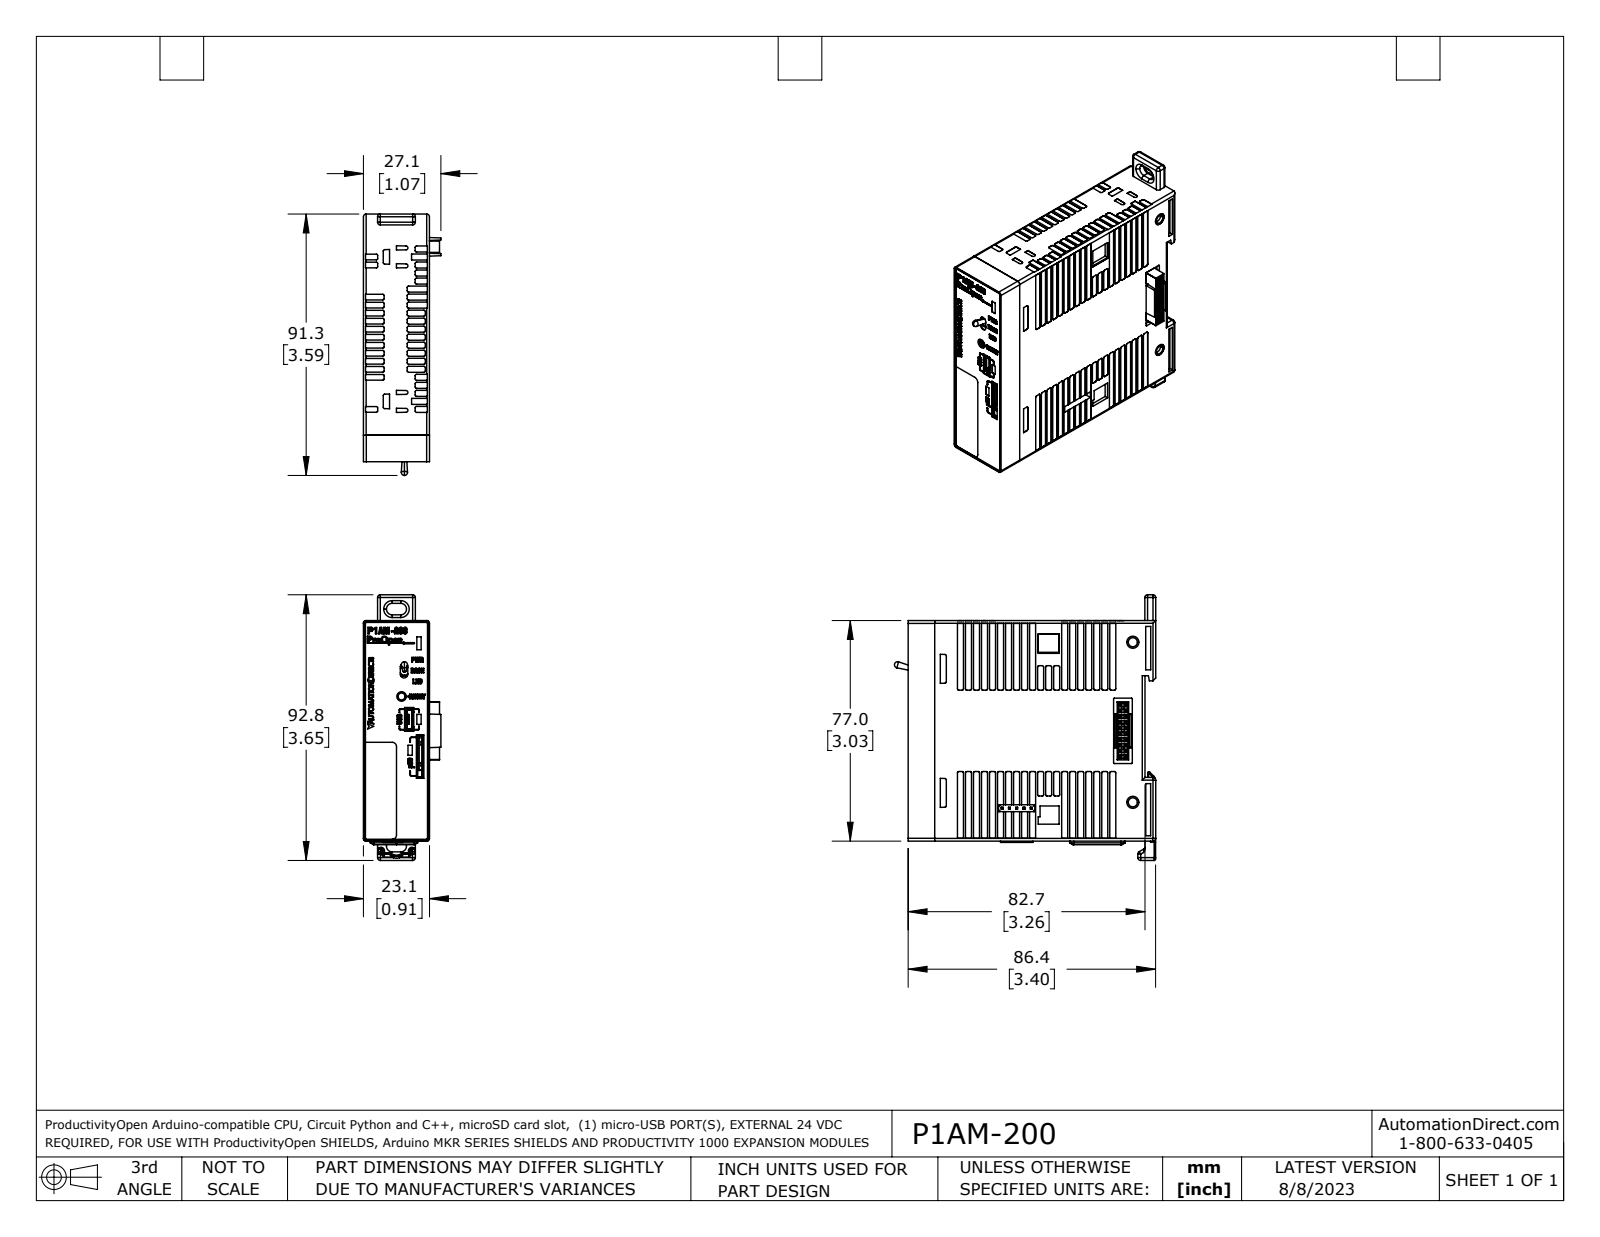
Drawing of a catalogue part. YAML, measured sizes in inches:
part_name: "P1AM-200 from P1AM-100 Br1 Coordfix n Mergw sketches 2c EXT1 comb1 New Mod WO FACE 1a B coord sr1 fxt"
step_written_by: "SolidWorks 2021 (AUTOMOTIVE_DESIGN)"
units: inches
bodies: {solids: 8, faces: 4984, planar: 3124, cylindrical: 705, other: 1155}
overall_size: [3.652, 3.593, 1.065]
volume: 8.409
surface_area: 52.15
round_holes:
  - {diameter: 0.024, count: 8}
  - {diameter: 0.012, count: 5}
  - {diameter: 0.009, count: 2}
  - {diameter: 0.01, count: 2}
  - {diameter: 0.016, count: 2}
  - {diameter: 0.124, count: 2}
  - {diameter: 0.159, count: 2}
  - {diameter: 0.166, count: 2}
  - {diameter: 0.008, count: 1}
  - {diameter: 0.095, count: 1}
  - {diameter: 0.123, count: 1}
round_bosses_or_shafts:
  - {diameter: 0.016, count: 3}
  - {diameter: 0.043, count: 2}
  - {diameter: 0.031, count: 2}
  - {diameter: 0.018, count: 2}
  - {diameter: 0.235, count: 1}
  - {diameter: 0.186, count: 1}
  - {diameter: 0.138, count: 1}
  - {diameter: 0.13, count: 1}
partial_cylinders:
  - {radius: 0.01, count: 128}
  - {radius: 0.02, count: 79}
  - {radius: 0.008, count: 40}
  - {radius: 0.006, count: 32}
  - {radius: 0.012, count: 21}
  - {radius: 0.009, count: 20}
  - {radius: 0.004, count: 17}
  - {radius: 0.039, count: 17}
face_to_face_distances: [0.908, 0.907, 0.349, 0.067, 0.361, 3.031, 0.842, 0.906, 3.039, 3.388]
hole_center_spacings: [0.079, 0.1, 0.157, 0.176, 0.2, 0.551, 0.557, 0.113]
